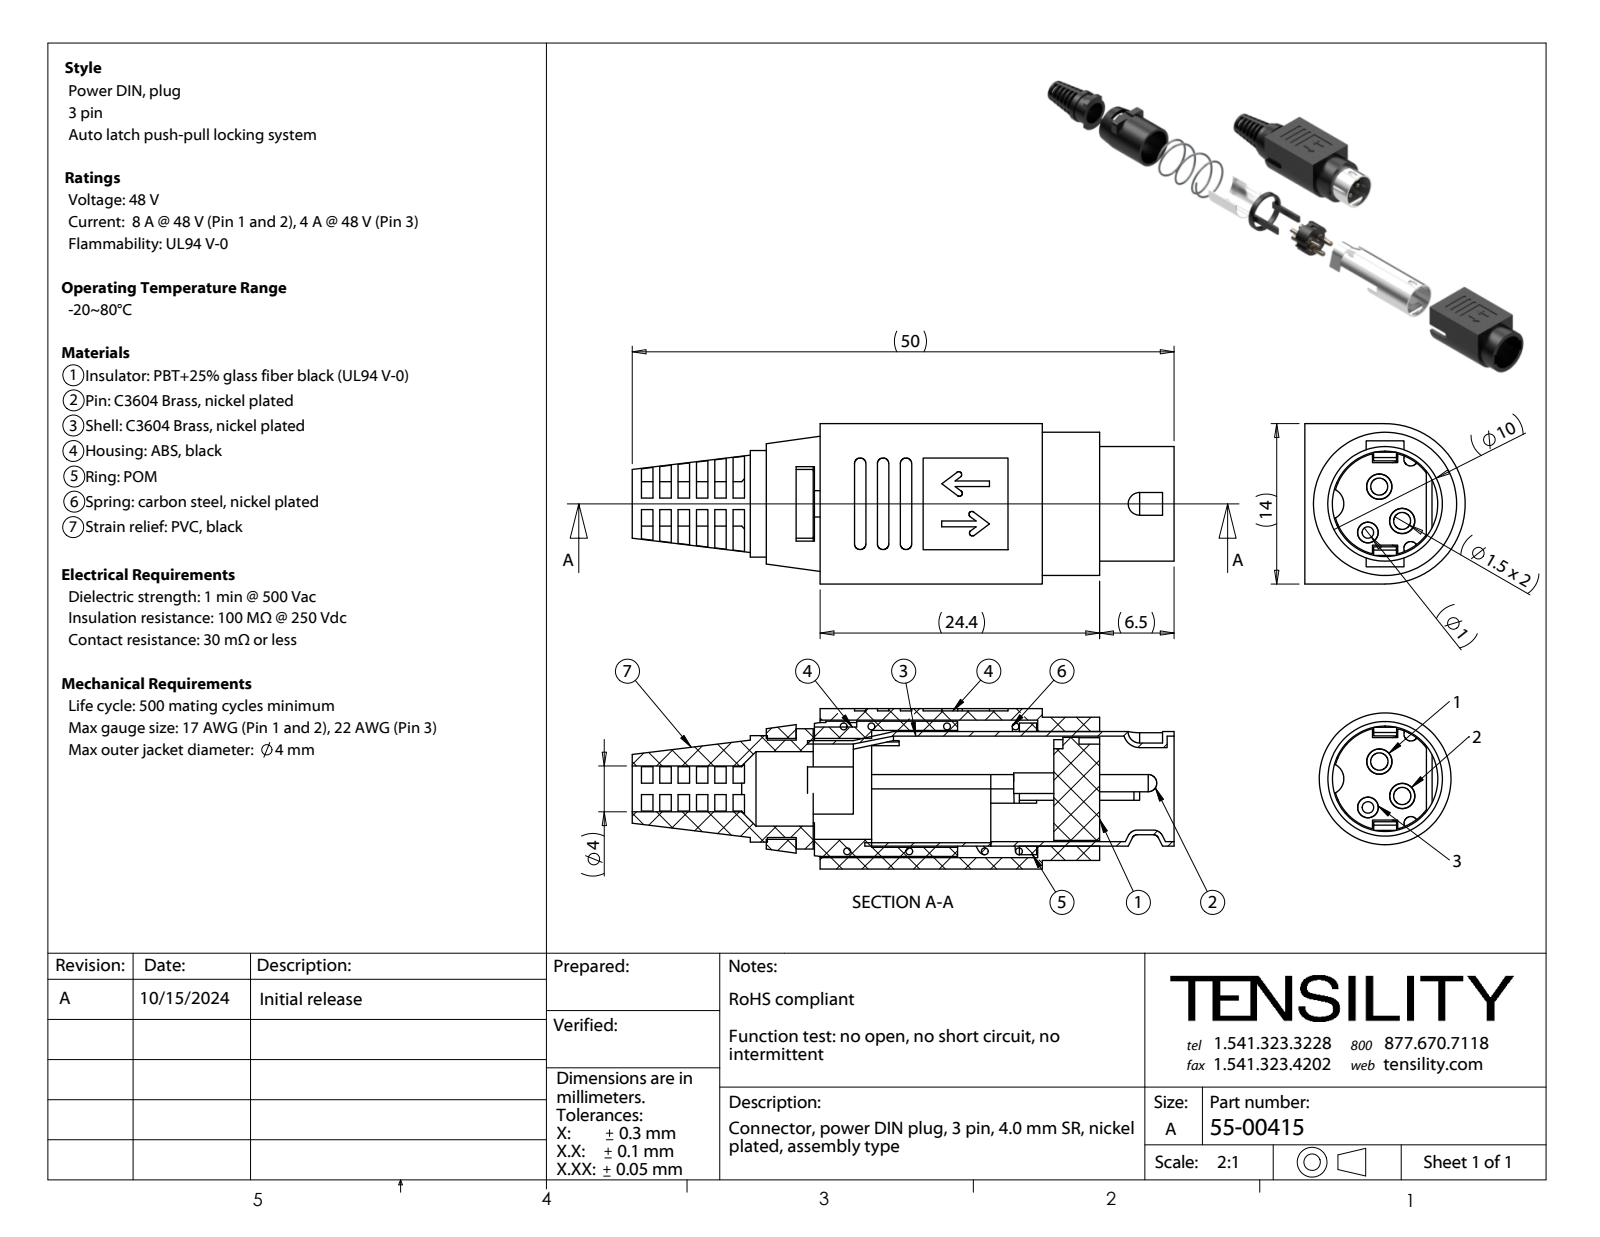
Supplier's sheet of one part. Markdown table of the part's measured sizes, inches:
| quantity | value |
| --- | --- |
| part name | 55-00415-07_默认; 55-00415-06_默认; 55-00415; 55-00415-05_默认 (+7 more) |
| STEP written by | SolidWorks 2025 (CONFIG_CONTROL_DESIGN) |
| units | inches |
| bodies | 11 solids, 403 faces (266 planar, 111 cylindrical, 26 other) |
| overall size | 1.862 × 0.551 × 0.551 |
| volume | 0.163 in³ |
| surface area | 11.43 in² |
| round holes (diameter × count) | 0.047 × 2, 0.028 × 1, 0.157 × 1, 0.256 × 1, 0.346 × 1, 0.362 × 1, 0.394 × 1, 0.402 × 1 |
| round bosses / shafts (diameter × count) | 0.071 × 3, 0.087 × 2, 0.059 × 2, 0.492 × 1, 0.465 × 1, 0.453 × 1, 0.366 × 1, 0.354 × 1 |
| partial cylindrical surfaces (radius × count) | 0.02 × 8, 0.039 × 4, 0.024 × 3, 0.01 × 2, 0.01 × 2, 0.035 × 2, 0.055 × 1, 0.059 × 1 |
| main face-to-face distances | 0.039, 0.512, 0.059, 0.063, 0.02, 0.472, 0.197, 0.217, 0.276, 0.024 |
| hole center spacings | 0.062, 0.083, 0.115, 0.124, 0.142, 0.162 |
